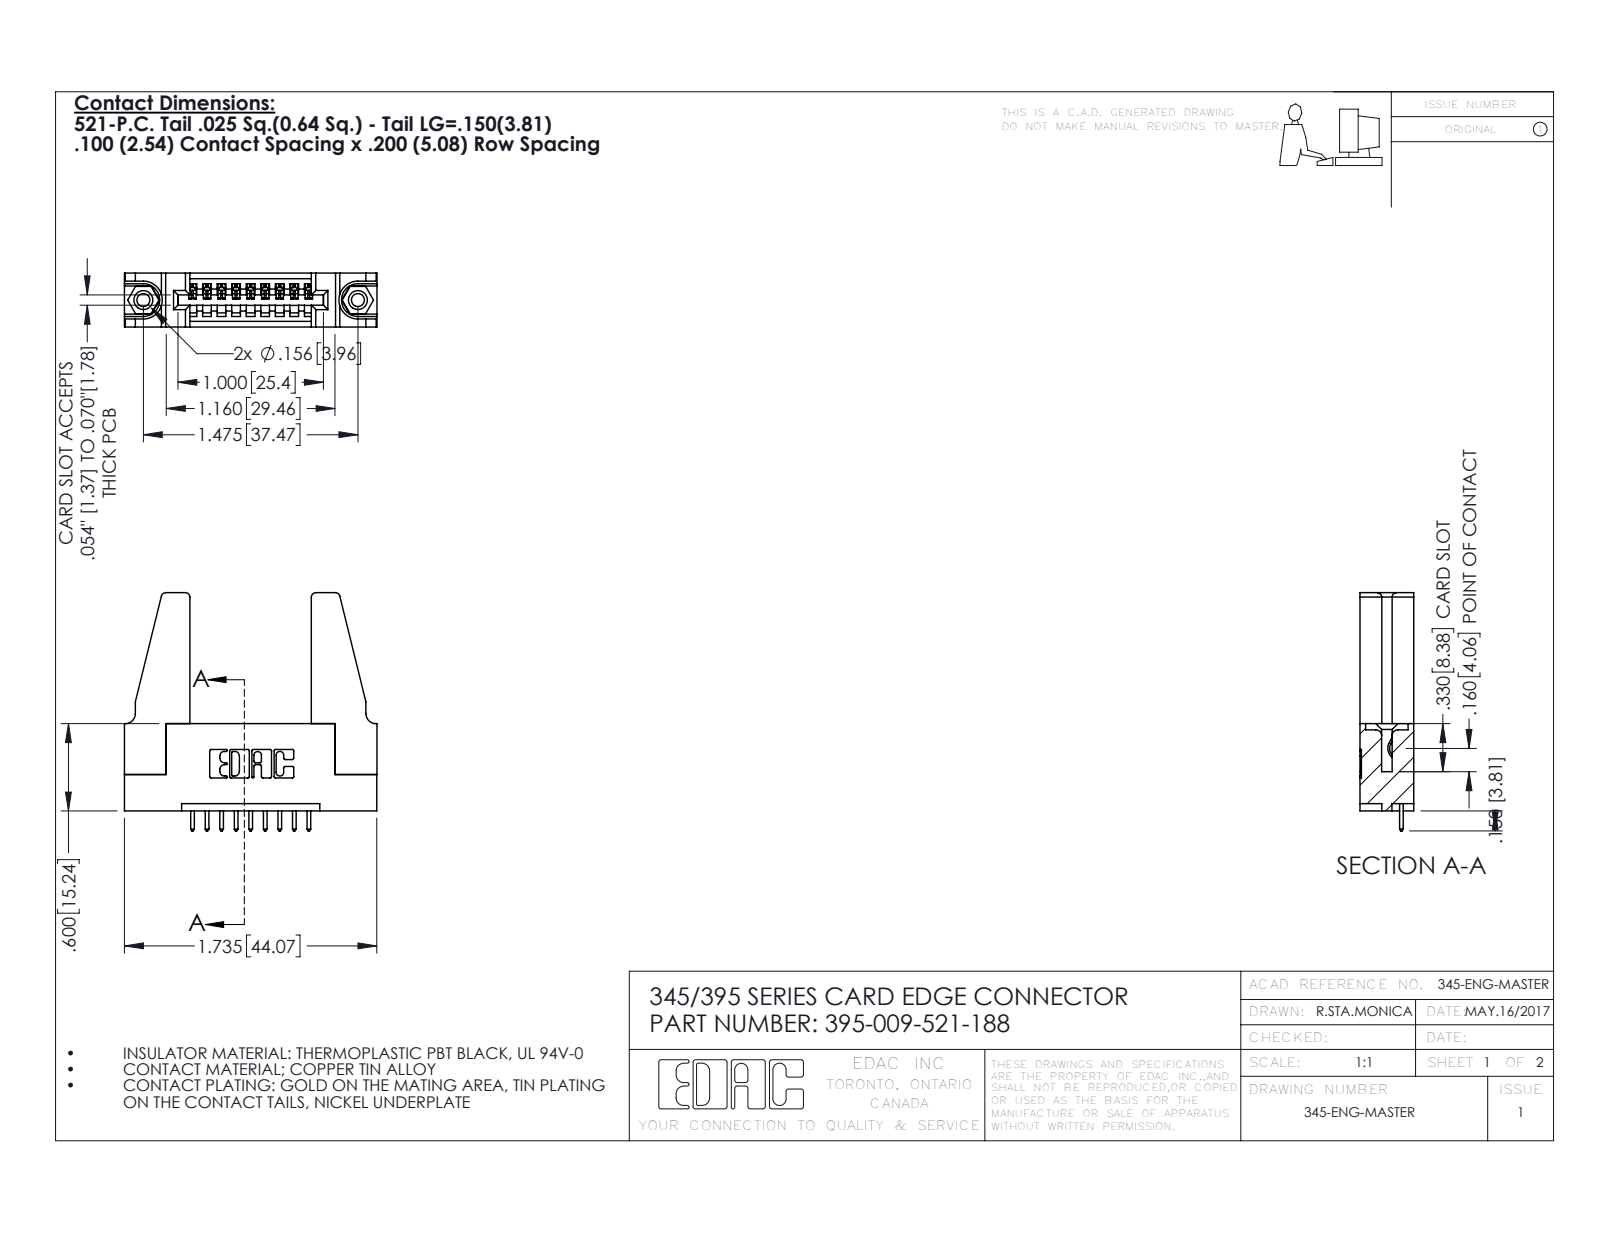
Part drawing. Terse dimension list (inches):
name: 345-220-078_345-220-088; 345 Part_Flush Mounting Lugs - 0.156 Dia-TH; 345-250-001_345-250-001-102; 395-009-521-188 (+1 more)
written by: SolidWorks 2016 (CONFIG_CONTROL_DESIGN)
unit: in
bodies: 14 solids, 772 faces (512 planar, 244 cylindrical, 16 other)
size: 1.736 × 1.637 × 0.37
volume: 0.436 in³; area: 12.02 in²
holes: 2× ⌀0.089, 2× ⌀0.125, 2× ⌀0.156, 1× ⌀0.064
bosses: 2× ⌀0.155
rounds: 22× R0.01, 18× R0.006, 18× R0.01, 8× R0.03, 6× R0.007, 6× R0.031, 3× R0.026, 2× R0.031
face distances: 0.37, 0.072, 0.298, 0.2, 0.098, 0.272, 0.025, 0.15, 0.148, 0.25
hole spacings: 0.27, 1.244, 1.475
